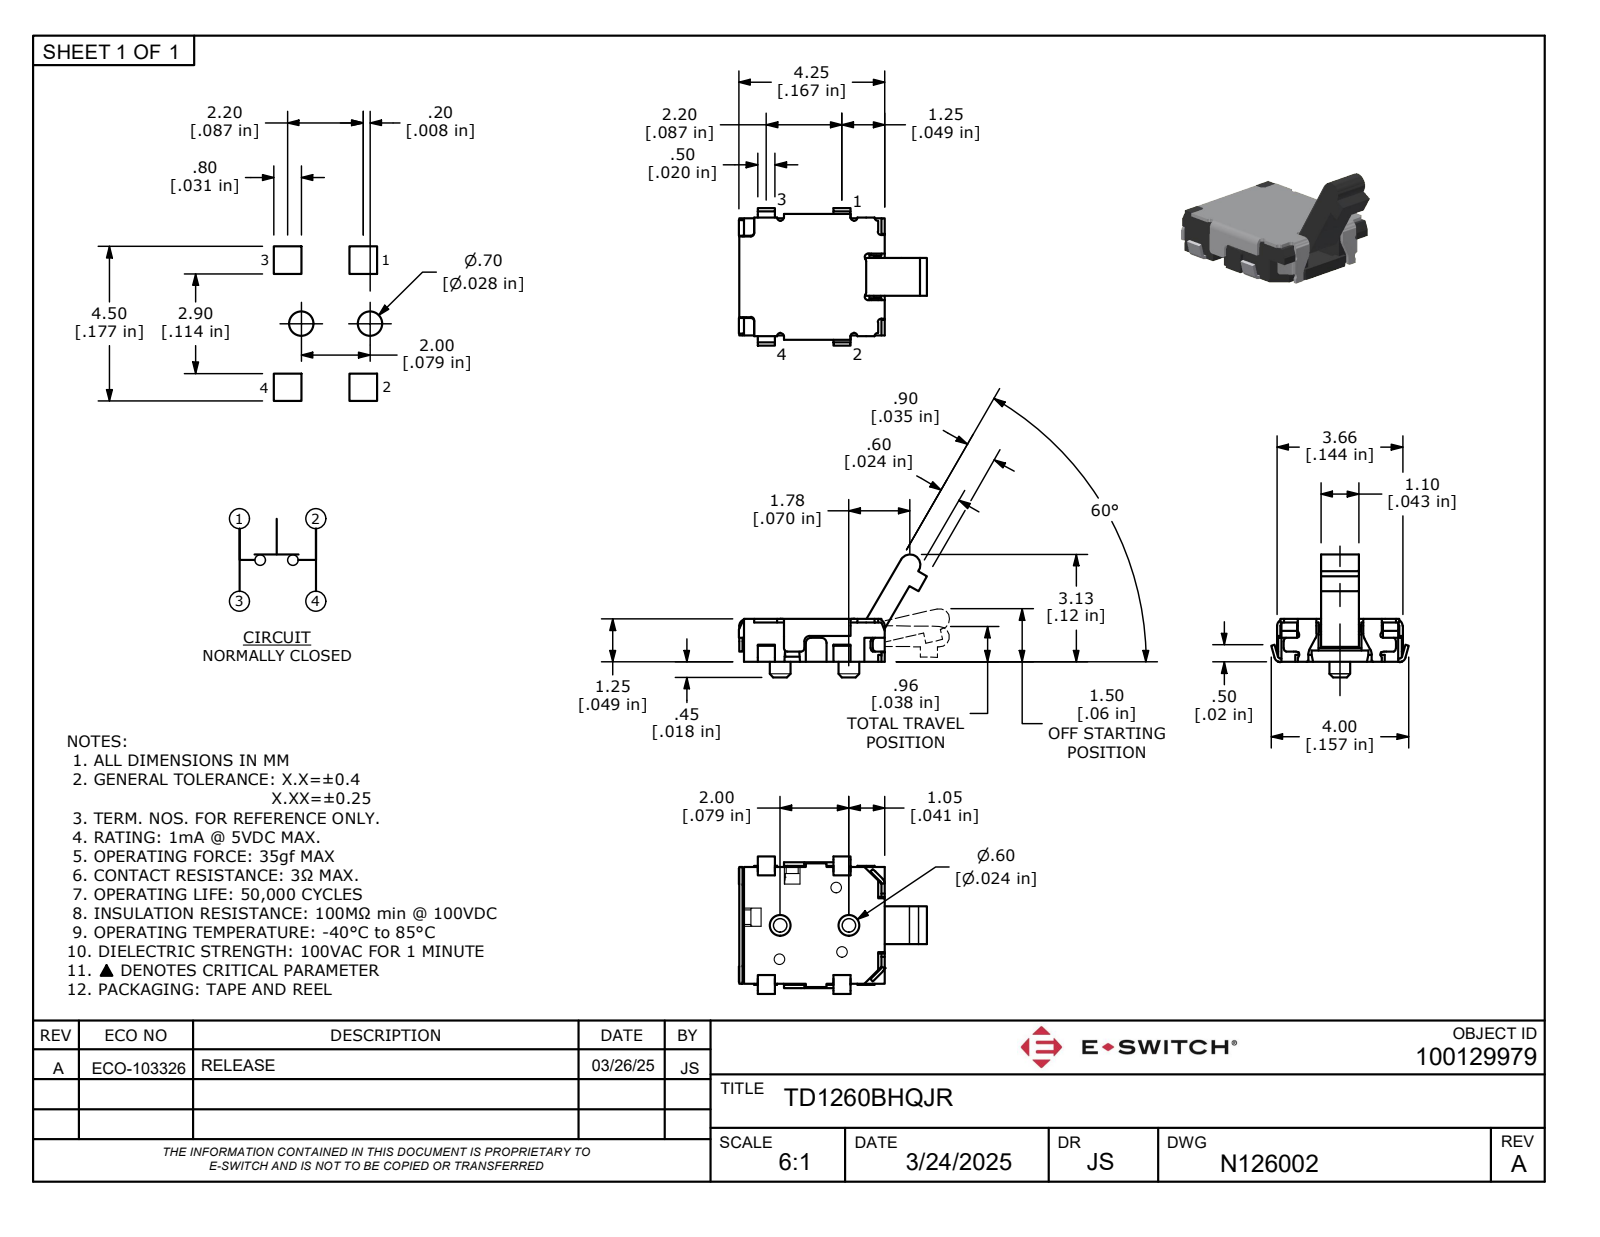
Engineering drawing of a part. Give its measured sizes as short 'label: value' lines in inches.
name: TD1260BHQJR
written by: Autodesk Inventor 2022 (AUTOMOTIVE_DESIGN)
unit: in
bodies: 1 solid, 426 faces (306 planar, 114 cylindrical, 6 other)
size: 0.216 × 0.157 × 0.141
volume: 0.001 in³; area: 0.167 in²
holes: 4× ⌀0.02, 3× ⌀0.012, 1× ⌀0.017
bosses: 2× ⌀0.024, 1× ⌀0.016, 1× ⌀0.008
rounds: 36× R0.004, 15× R0.008, 5× R0.012, 4× R0.006, 3× R0.007, 1× R0.005, 1× R0.014, 1× R0.02
face distances: 0.049, 0.045, 0.033, 0.016, 0.03, 0.043, 0.089, 0.134, 0.046, 0.122
hole spacings: 0.018, 0.033, 0.035, 0.072, 0.074, 0.083, 0.084, 0.085
